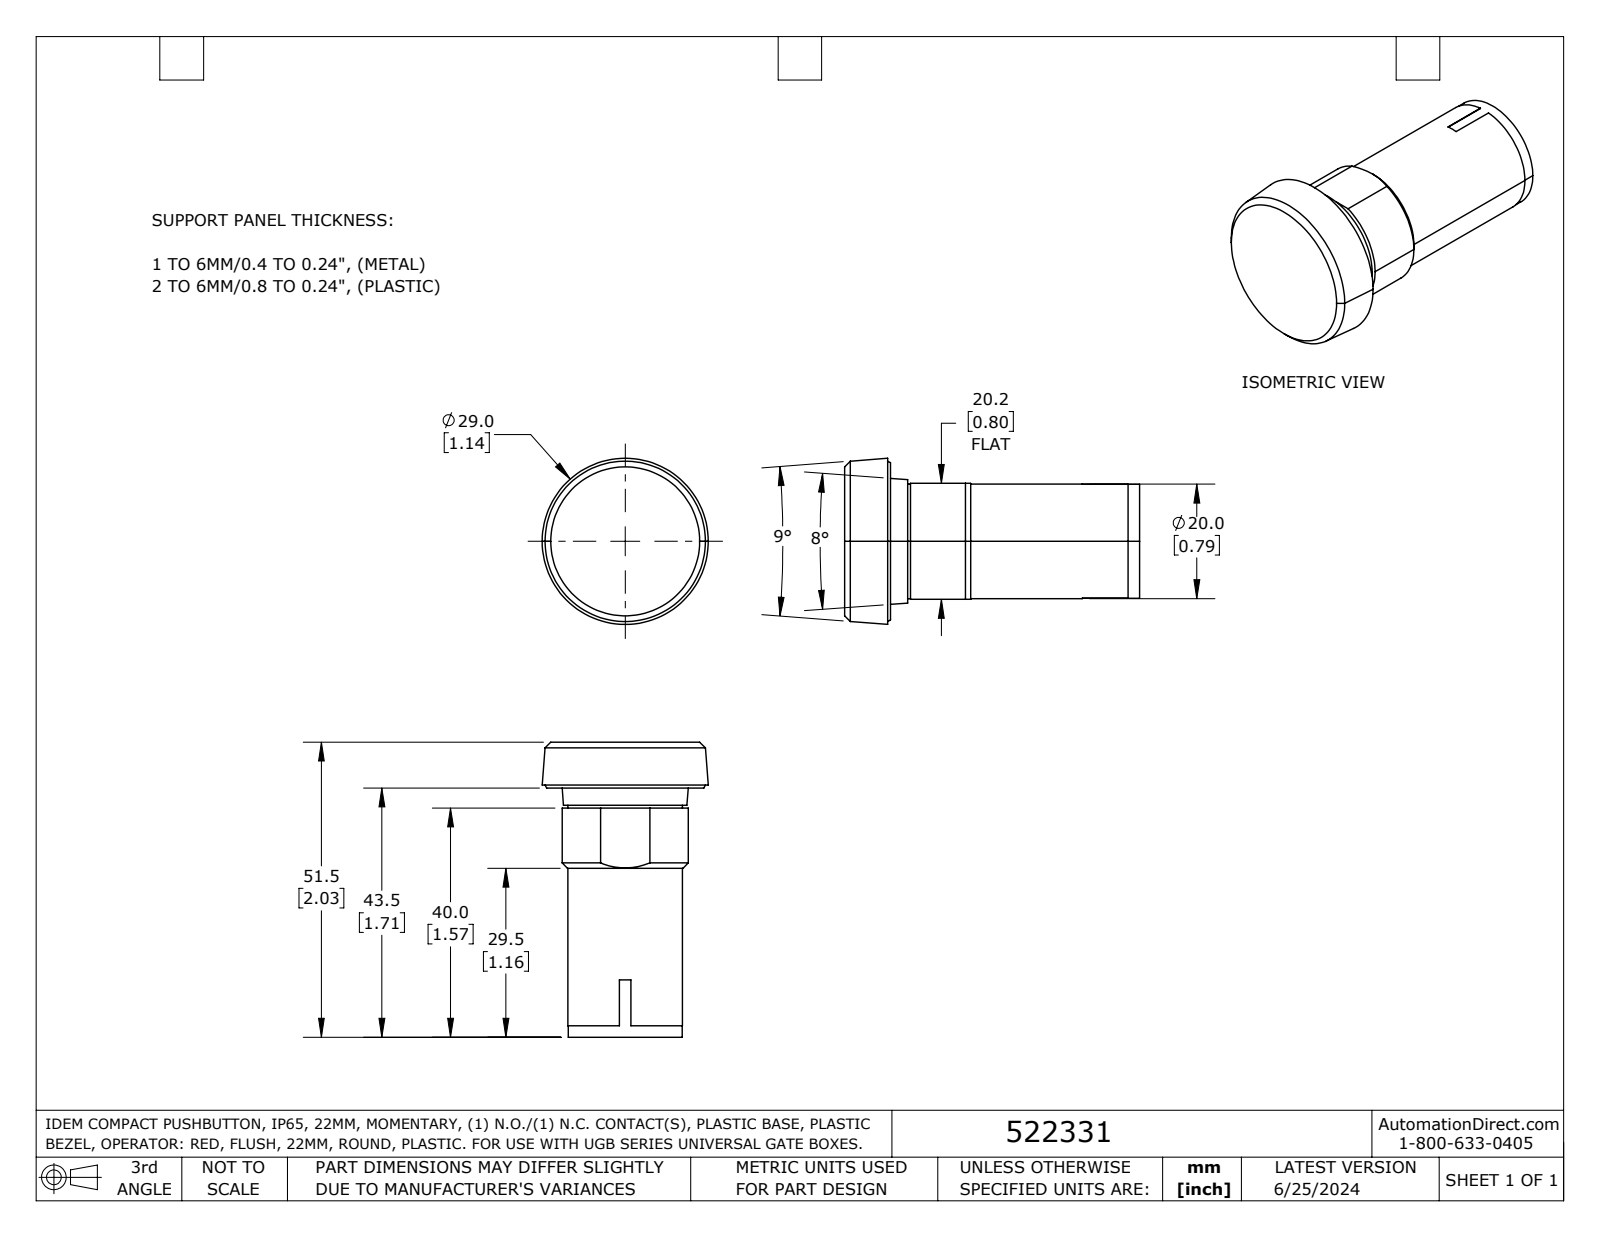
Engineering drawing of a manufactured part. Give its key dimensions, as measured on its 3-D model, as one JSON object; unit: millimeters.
{"part_name": "522331", "step_written_by": "SolidWorks 2023 (AUTOMOTIVE_DESIGN)", "units": "millimeters", "bodies": {"solids": 1, "faces": 37, "planar": 17, "cylindrical": 10, "other": 10}, "overall_size": [51.5, 29, 29], "volume_mm3": 19420, "surface_area_mm2": 4797, "round_bosses_or_shafts": [[20, 1], [19.9, 1]], "partial_cylinders_radius": [[11, 1]], "face_to_face_distances": [51.5, 8, 43.5, 3.5, 0.5, 20.2, 11, 11.5, 40, 3]}
